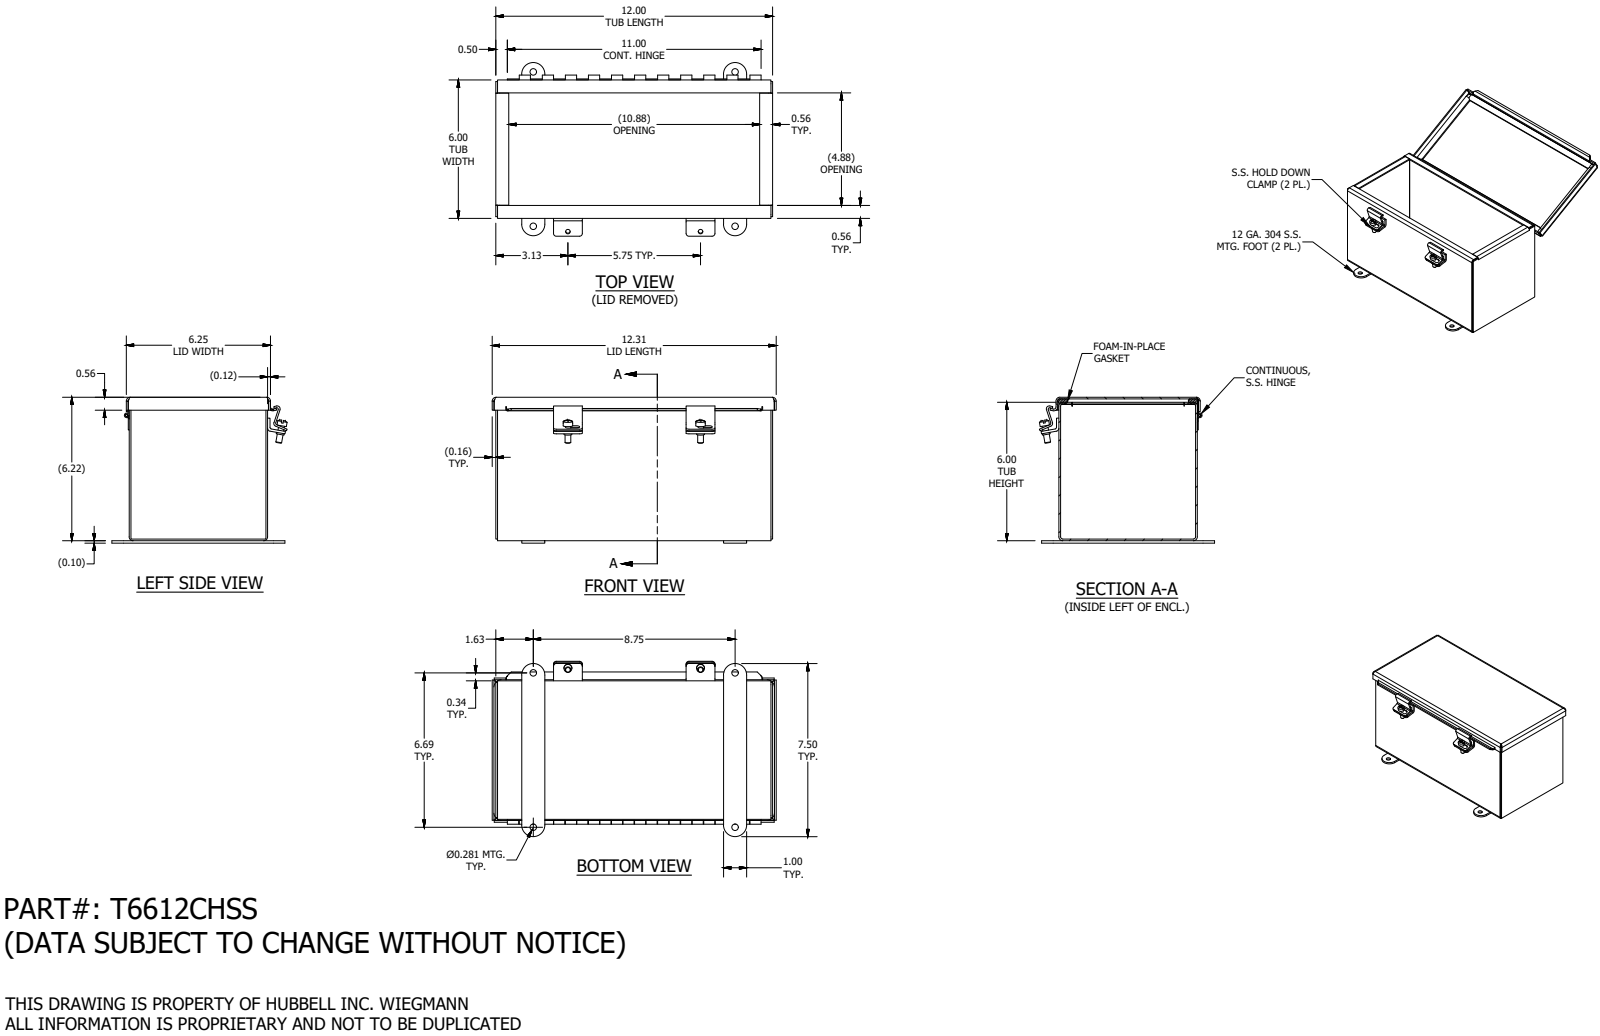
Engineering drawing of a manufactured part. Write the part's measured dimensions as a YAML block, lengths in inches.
part_name: "T6612CHSS"
step_written_by: "SolidWorks 2019 (AUTOMOTIVE_DESIGN)"
units: inches
bodies: {solids: 16, faces: 406, planar: 245, cylindrical: 129, other: 32}
overall_size: [12.313, 7.598, 6.322]
volume: 34.82
surface_area: 920.2
round_holes:
  - {diameter: 0.11, count: 4}
  - {diameter: 0.281, count: 4}
  - {diameter: 0.196, count: 2}
  - {diameter: 0.116, count: 1}
round_bosses_or_shafts:
  - {diameter: 0.41, count: 2}
  - {diameter: 0.344, count: 2}
  - {diameter: 0.25, count: 2}
  - {diameter: 0.2, count: 1}
  - {diameter: 0.1, count: 1}
partial_cylinders:
  - {radius: 0.094, count: 11}
  - {radius: 0.168, count: 11}
  - {radius: 0.085, count: 8}
  - {radius: 0.125, count: 8}
  - {radius: 0.133, count: 4}
  - {radius: 0.242, count: 4}
  - {radius: 0.5, count: 4}
  - {radius: 0.063, count: 3}
face_to_face_distances: [0.074, 5.926, 6.144, 6, 5.852, 6.218, 6.07, 11.926, 11.852, 12]
hole_center_spacings: [5.75, 0.75, 6.687, 8.75, 11.013, 5, 6.5]
